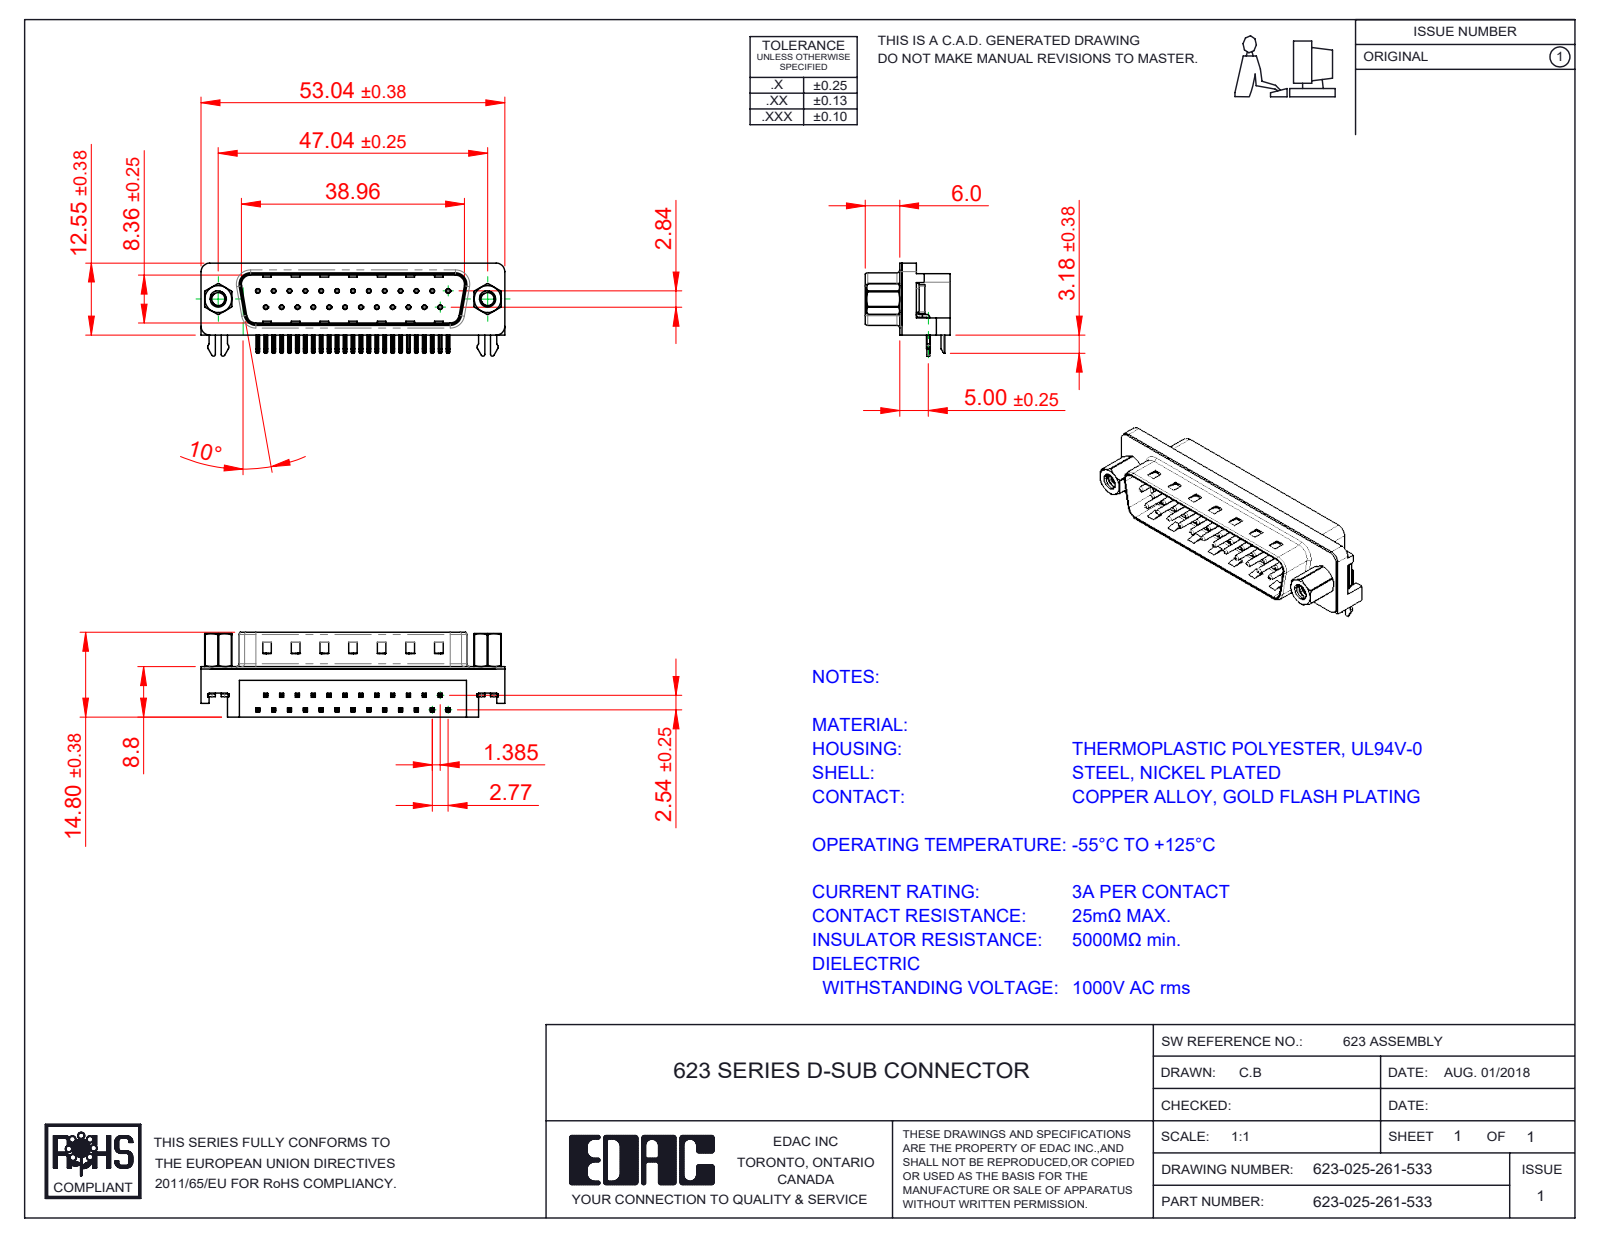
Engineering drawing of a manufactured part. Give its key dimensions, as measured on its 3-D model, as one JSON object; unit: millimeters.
{"part_name": "623-025-261-533; 623 Housing_25 Socket; 623 Contact Bottom; 623 4-40 Threaded Rivet (+4 more)", "step_written_by": "SolidWorks 2016 (CONFIG_CONTROL_DESIGN)", "units": "millimeters", "bodies": {"solids": 33, "faces": 2409, "planar": 1455, "cylindrical": 721, "other": 233}, "overall_size": [53.04, 16.25, 14.8], "volume_mm3": 4942, "surface_area_mm2": 7249, "round_holes": [[0.35, 25], [0.8, 25], [2.26, 2], [2.29, 2], [4, 2], [4.8, 2], [5, 2]], "round_bosses_or_shafts": [[0.75, 25], [4.9, 2], [4.75, 2], [3.9, 2], [2.79, 2]], "partial_cylinders_radius": [[0.25, 108], [0.12, 50], [0.5, 14], [1, 8], [1.5, 7], [0.32, 4], [0.9, 4], [1.6, 4]], "face_to_face_distances": [0.4, 8.4, 2.1, 1.7, 8.76, 10.46, 10.86, 8.8, 10.35, 5.9], "hole_center_spacings": [3.16, 2.77, 11.08, 5.54, 8.31, 5.03, 13.85, 7.48]}
